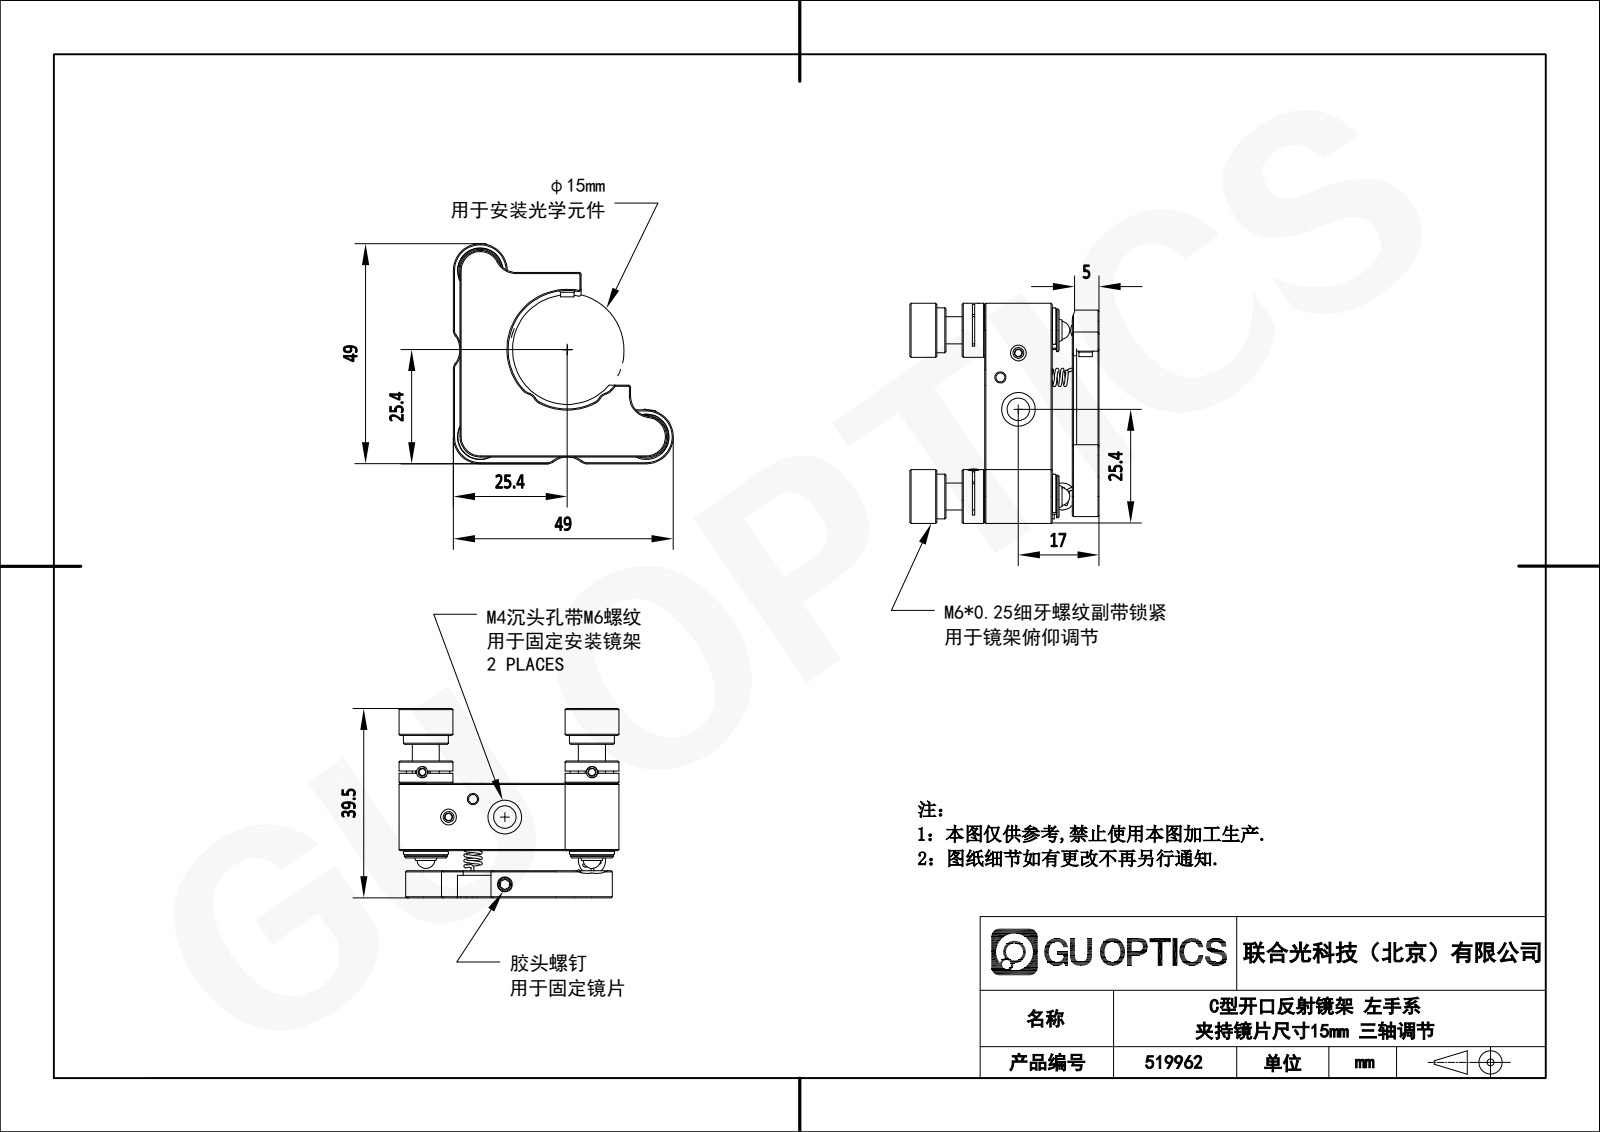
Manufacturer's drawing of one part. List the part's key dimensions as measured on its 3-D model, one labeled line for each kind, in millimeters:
STEP written by: SolidWorks 2021 (CONFIG_CONTROL_DESIGN)
Units: millimetres
Bodies: 0 solids, 516 faces (161 planar, 147 cylindrical, 208 other)
Overall size (bounding box): 49 × 49 × 40.43
Round holes (diameter × count): ⌀4 ×3, ⌀2.5 ×2, ⌀5 ×2, ⌀6 ×2, ⌀7.5 ×2, ⌀3.3 ×1, ⌀5.5 ×1
Round bosses / shafts (diameter × count): ⌀3 ×8, ⌀12 ×3, ⌀10 ×3, ⌀9.5 ×3, ⌀8 ×3, ⌀6 ×3, ⌀4 ×3
Partial cylindrical surfaces — rounded edges, fillets, slot ends (radius × count): R0.2 ×8, R1.5 ×6, R4.5 ×6, R0.5 ×4, R2 ×4, R5 ×2, R10 ×2, R7 ×1
Main face-to-face distances: 6, 25, 4, 19, 10, 15, 1.5, 2.25, 2.75, 34.43
Hole centre spacings: 8.15, 10.5, 26.5, 37, 45.51, 14.5, 19.82, 37.48
